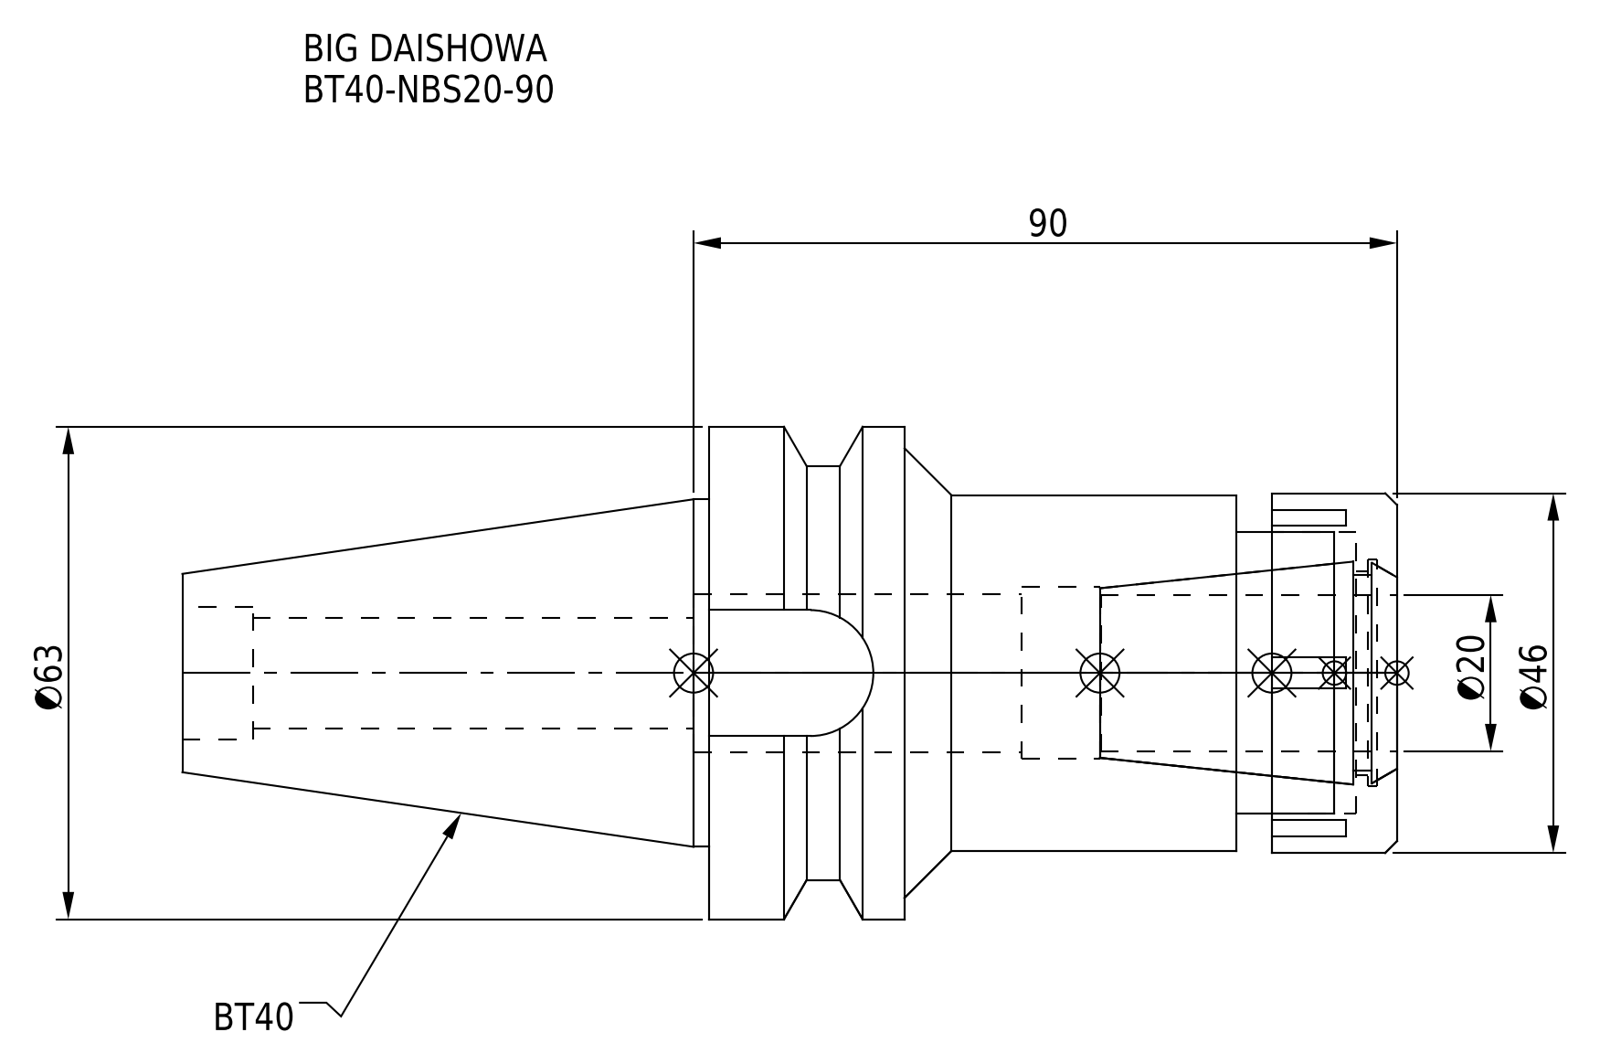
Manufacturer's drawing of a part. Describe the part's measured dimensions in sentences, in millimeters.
The part is named "NBN20_1.stp; BT40NB20090-200_ASM.stp; DXF_TEMP_ASSY_ASM_4_ASM.stp; BT40-NBS20-90 (+3 more)". Its 3-D file was written by "SolidWorks 2019 (CONFIG_CONTROL_DESIGN)". It is 2 solids with 88 faces: 44 planar, 30 cylindrical and 14 other. Overall it measures 155.4 by 63 by 63 millimeters. Its volume is 187 774 cubic millimeters and its surface area 40 660 square millimeters. Round holes: 1 of diameter 14.2, 1 of diameter 17, 1 of diameter 20.3, 1 of diameter 22, 1 of diameter 26, 1 of diameter 29, 1 of diameter 36. Round bosses or shafts: 1 of diameter 63, 1 of diameter 53, 1 of diameter 46, 1 of diameter 45.5, 1 of diameter 44.45. Partial cylindrical surfaces (rounded edges, fillets, slot ends): 1 of radius 8.05. The main face-to-face distances are 88, 8, 20.5, 67.5, 42.5, 16, 4.5, 72, 25, 63.
